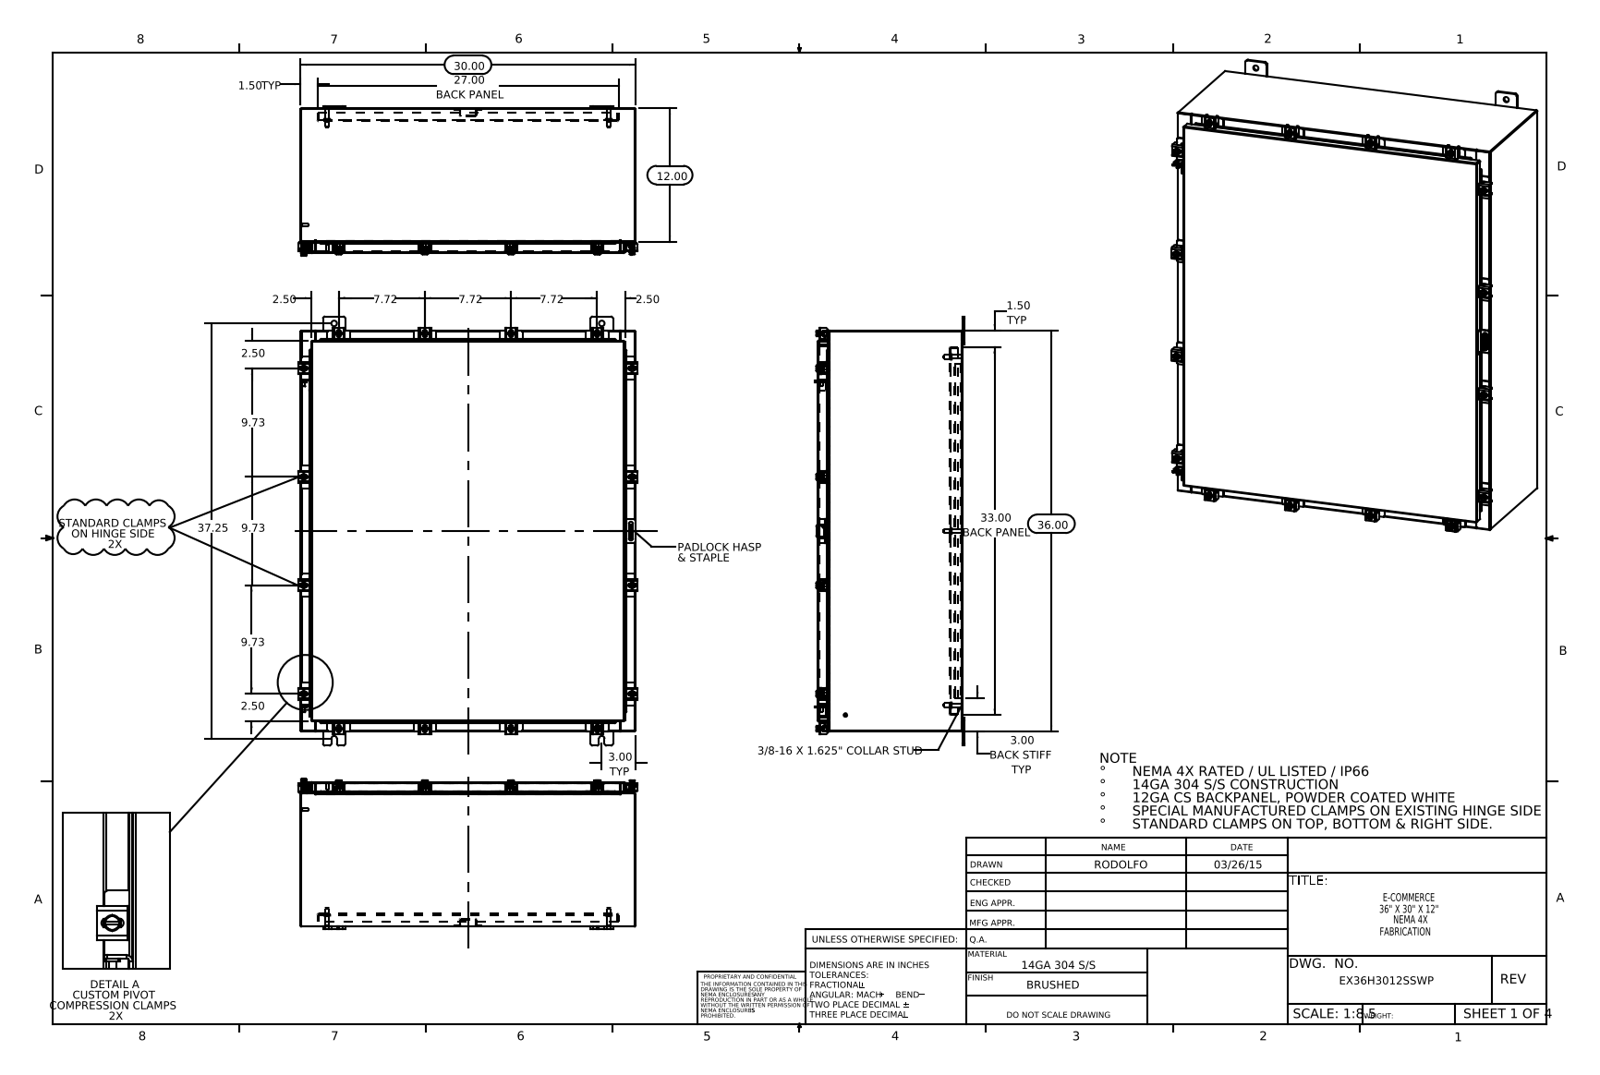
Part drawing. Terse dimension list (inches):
name: EX36H3012SSWP Mounting Studs; EX36H3012SSWP Cover; N-WMT04X30402202210-00 Clamp Top; Quarter-20 CD Stud (+8 more)
written by: SolidWorks 2014 (CONFIG_CONTROL_DESIGN)
unit: in
bodies: 109 solids, 2711 faces (1431 planar, 1060 cylindrical, 220 other)
size: 38.5 × 30.421 × 13.453
volume: 421.1 in³; area: 10 507 in²
holes: 17× ⌀0.213, 17× ⌀0.26, 10× ⌀0.5, 1× ⌀0.125, 1× ⌀0.25
bosses: 17× ⌀0.5, 17× ⌀0.25, 15× ⌀0.399, 6× ⌀0.625, 6× ⌀0.375, 6× ⌀0.33, 2× ⌀0.315, 2× ⌀0.236
rounds: 74× R0.06, 34× R0.141, 32× R0.12, 30× R0.013, 26× R0.088, 24× R0.09, 24× R0.19, 23× R0.05
face distances: 0.075, 12.9, 12.826, 12.975, 0.104, 1, 1.075, 11.826, 11.9, 1.179
hole spacings: 31.017, 35.451, 2.347, 4.44, 5.299, 9.73, 10.964, 13.241
